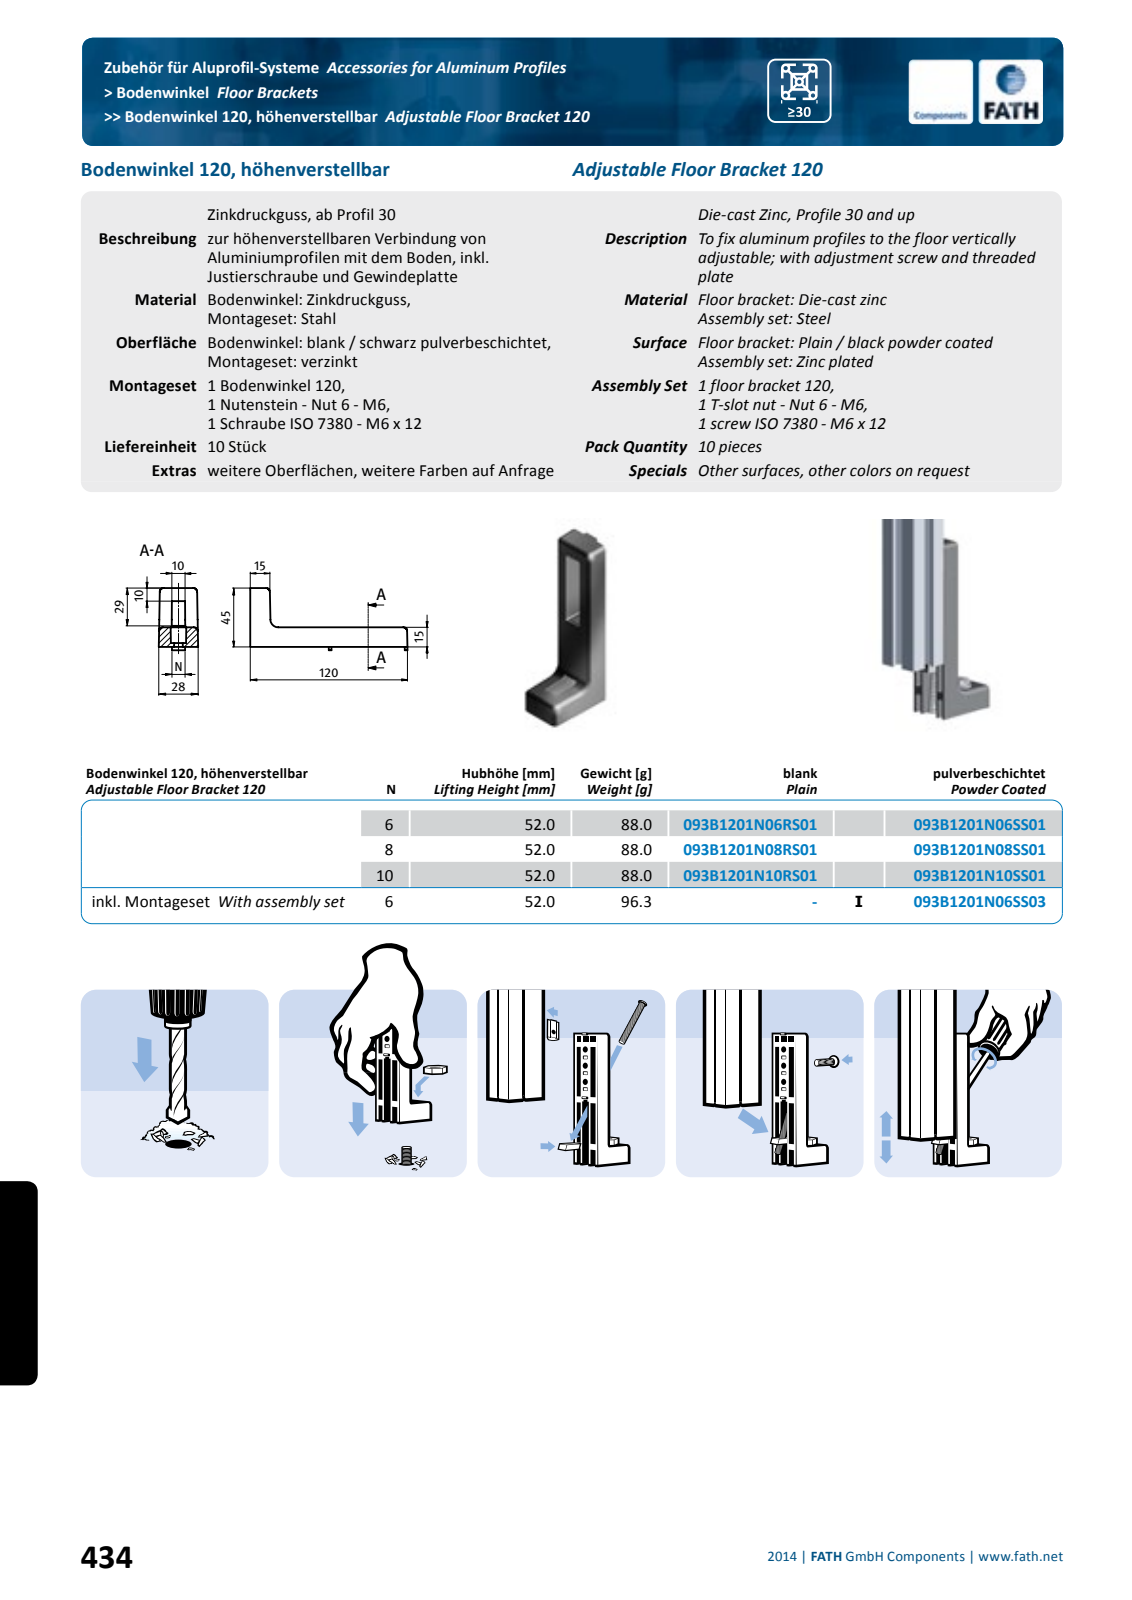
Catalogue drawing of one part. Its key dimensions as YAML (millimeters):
part_name: "fath_093b1201n08ss01_1; fath_093b1201n08ss01_2; fath_093b1201n08ss01_3"
step_written_by: "Spatial InterOp 3D (automotive_design)"
units: millimeters
bodies: {solids: 3, faces: 292, planar: 95, cylindrical: 89, other: 108}
overall_size: [120.84, 53.28, 28.2]
volume: 30418
surface_area: 24676
round_holes:
  - {diameter: 5, count: 1}
  - {diameter: 6.1, count: 1}
round_bosses_or_shafts:
  - {diameter: 11, count: 1}
partial_cylinders:
  - {radius: 0.5, count: 20}
  - {radius: 1.01, count: 14}
  - {radius: 0.5, count: 13}
  - {radius: 3.02, count: 10}
  - {radius: 6.04, count: 1}
face_to_face_distances: [20.12, 2.02, 15.11, 7.76, 12.13, 19.89, 2.27, 14.4, 22.16, 20.14]
